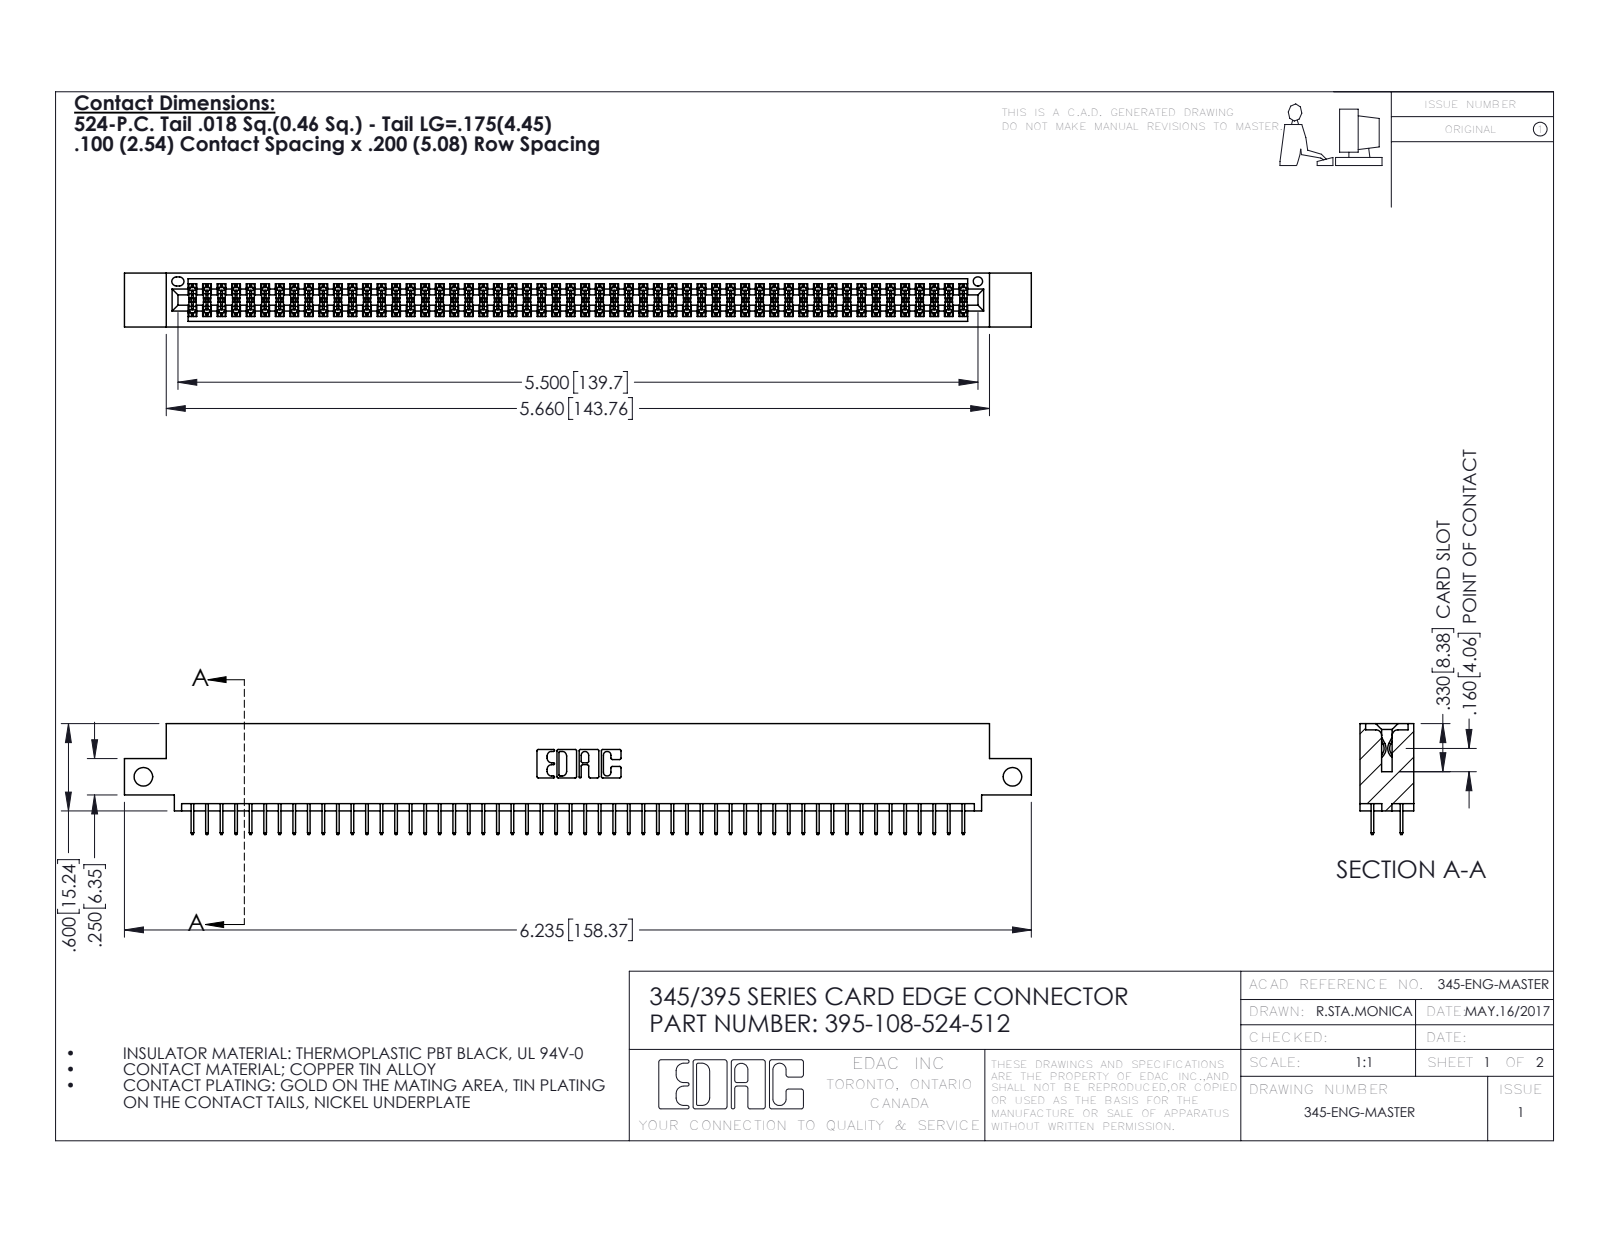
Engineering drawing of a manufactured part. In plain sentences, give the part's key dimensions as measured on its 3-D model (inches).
The part is named "345 Part_0.110 Offset - Side Mount; 345-292-001_345-293-124; 395-108-524-512". Its 3-D file was written by "SolidWorks 2016 (CONFIG_CONTROL_DESIGN)". It is 109 solids with 5962 faces: 4296 planar, 1666 cylindrical and 0 other. Overall it measures 6.235 by 0.762 by 0.37 inches. Its volume is 0.926 cubic inches and its surface area 34.39 square inches. Round holes: 2 of diameter 0.128, 1 of diameter 0.064. Partial cylindrical surfaces (rounded edges, fillets, slot ends): 162 of radius 0.006, 22 of radius 0.01, 6 of radius 0.007, 6 of radius 0.031, 3 of radius 0.026, 2 of radius 0.014, 2 of radius 0.019, 2 of radius 0.022. The main face-to-face distances are 0.072, 0.298, 0.2, 0.37, 0.098, 0.272, 0.025, 0.225, 0.072, 0.175. The hole center spacings are 5.975.
